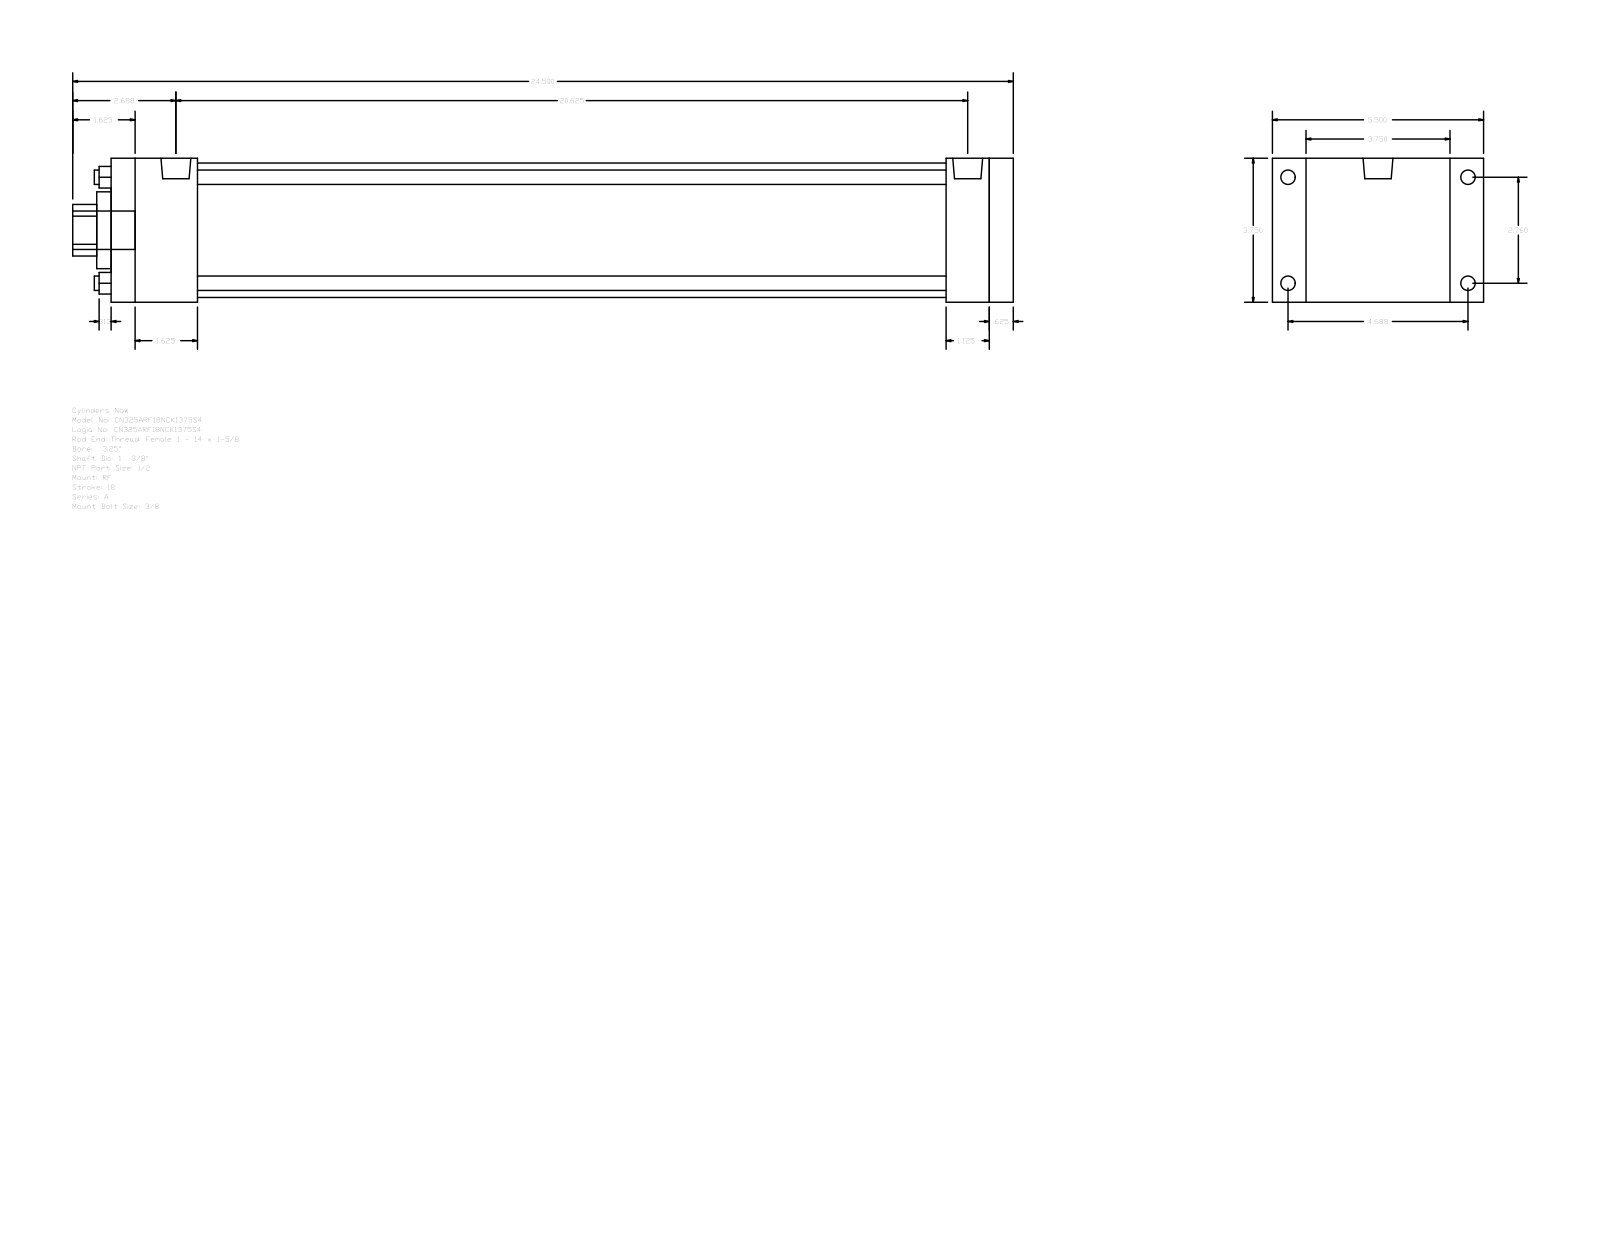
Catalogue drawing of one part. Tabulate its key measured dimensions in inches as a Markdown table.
| quantity | value |
| --- | --- |
| part name | A_RF__0325_1.375 |
| STEP written by | GSSL Pune (CONFIG_CONTROL_DESIGN) |
| units | inches |
| bodies | 0 solids, 92 faces (64 planar, 28 cylindrical, 0 other) |
| overall size | 24.5 × 5.5 × 3.75 |
| round holes (diameter × count) | 0.375 × 4, 1.375 × 1, 2 × 1, 3.5 × 1 |
| round bosses / shafts (diameter × count) | 0.375 × 4, 0.344 × 4, 0.778 × 2, 1 × 1 |
| partial cylindrical surfaces (radius × count) | 0.672 × 1 |
| main face-to-face distances | 3.75, 23.5, 0.625, 22.875, 0.875, 4.625, 1.125, 21.75, 1.75, 2.25 |
| hole center spacings | 1.952, 2.76, 3.903 |
